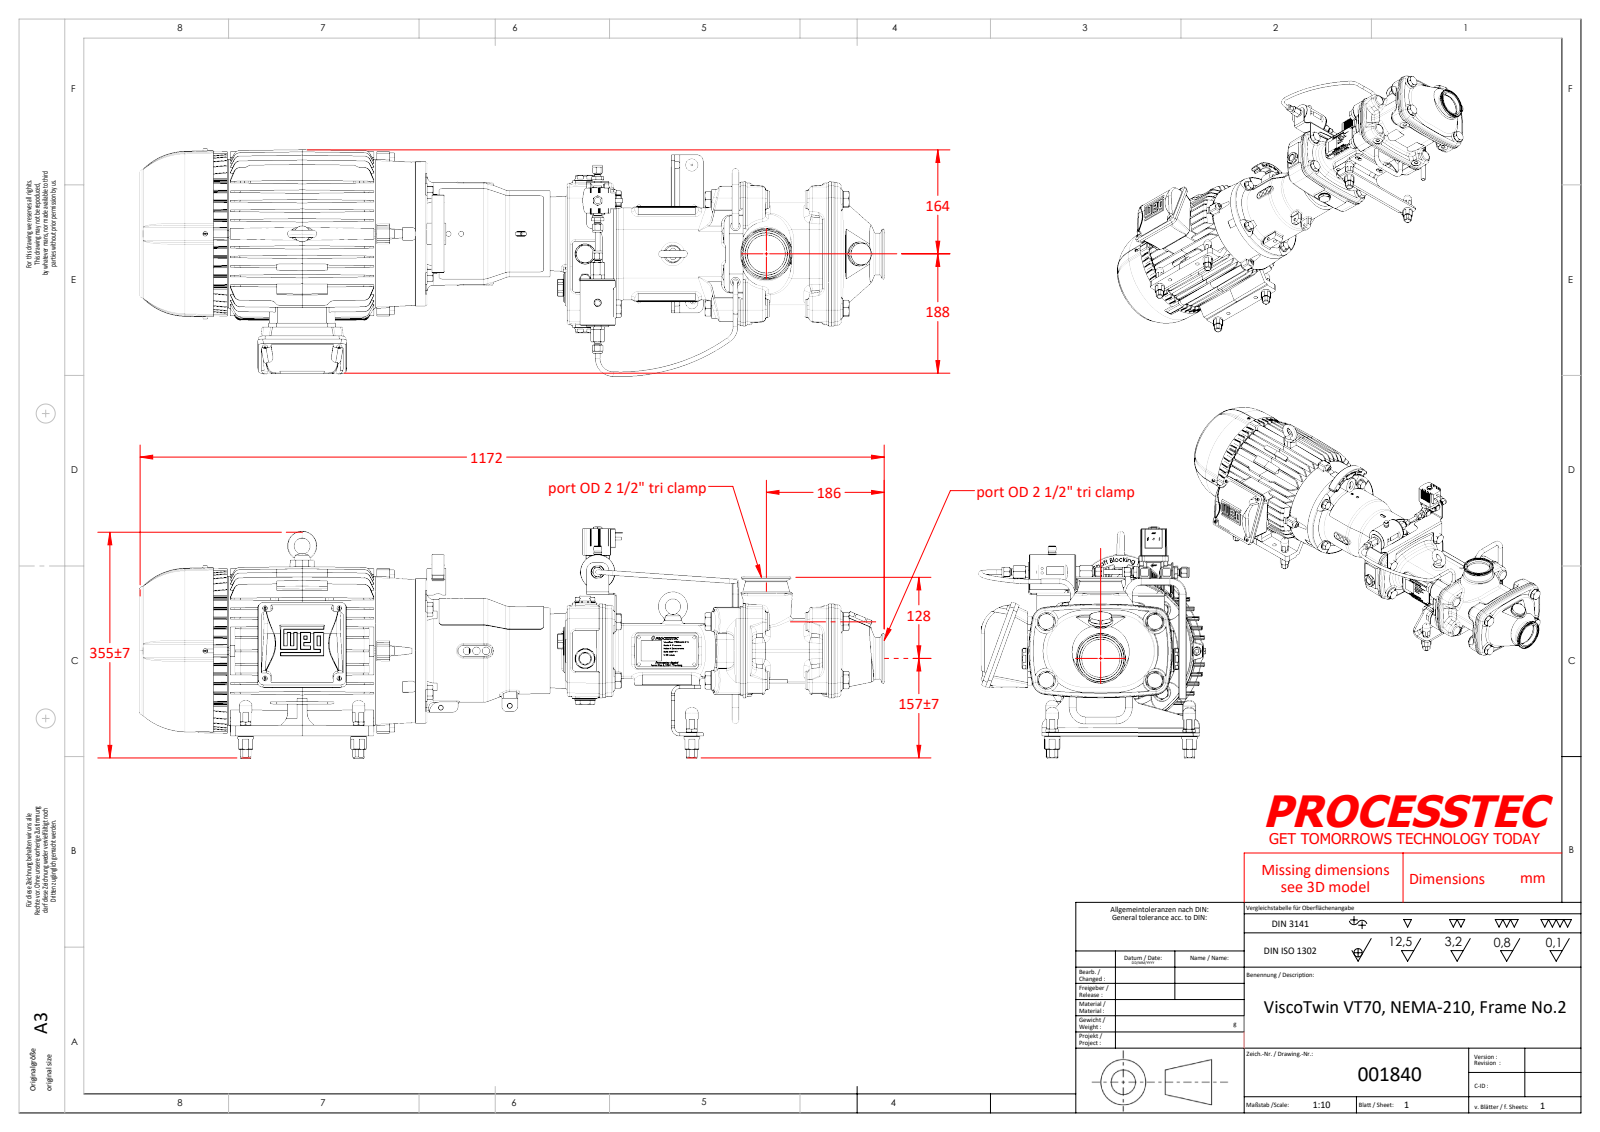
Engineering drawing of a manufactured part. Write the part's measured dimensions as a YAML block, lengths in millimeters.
part_name: "Twin Screw Pump VT70 on F2 with NEMA210 - 001840"
step_written_by: "SolidWorks 2023 (AUTOMOTIVE_DESIGN)"
units: millimeters
bodies: {solids: 120, faces: 14218, planar: 6631, cylindrical: 2945, other: 4642}
overall_size: [1171.9, 363.02, 357.26]
volume: 35390000
surface_area: 2707000
round_holes:
  - {diameter: 8, count: 17}
  - {diameter: 14, count: 10}
  - {diameter: 6, count: 9}
  - {diameter: 8.5, count: 9}
  - {diameter: 5, count: 8}
  - {diameter: 10.41, count: 8}
  - {diameter: 9, count: 7}
  - {diameter: 4, count: 6}
  - {diameter: 19.2, count: 6}
  - {diameter: 2.5, count: 5}
  - {diameter: 8.92, count: 5}
  - {diameter: 17.5, count: 5}
round_bosses_or_shafts:
  - {diameter: 24, count: 14}
  - {diameter: 10, count: 13}
  - {diameter: 16, count: 10}
  - {diameter: 19, count: 6}
  - {diameter: 5, count: 6}
  - {diameter: 28, count: 5}
  - {diameter: 6, count: 5}
  - {diameter: 40, count: 4}
partial_cylinders:
  - {radius: 1, count: 1156}
  - {radius: 3, count: 97}
  - {radius: 2, count: 65}
  - {radius: 5, count: 64}
  - {radius: 1.5, count: 46}
  - {radius: 8, count: 38}
  - {radius: 2.2, count: 24}
  - {radius: 10, count: 22}
face_to_face_distances: [15, 30, 5.5, 231.3, 102.4, 9.5, 20.5, 87.4, 117.4, 589.1]
hole_center_spacings: [83.08, 41, 45, 68.01, 68.14, 22.59, 41.01, 132.11]
